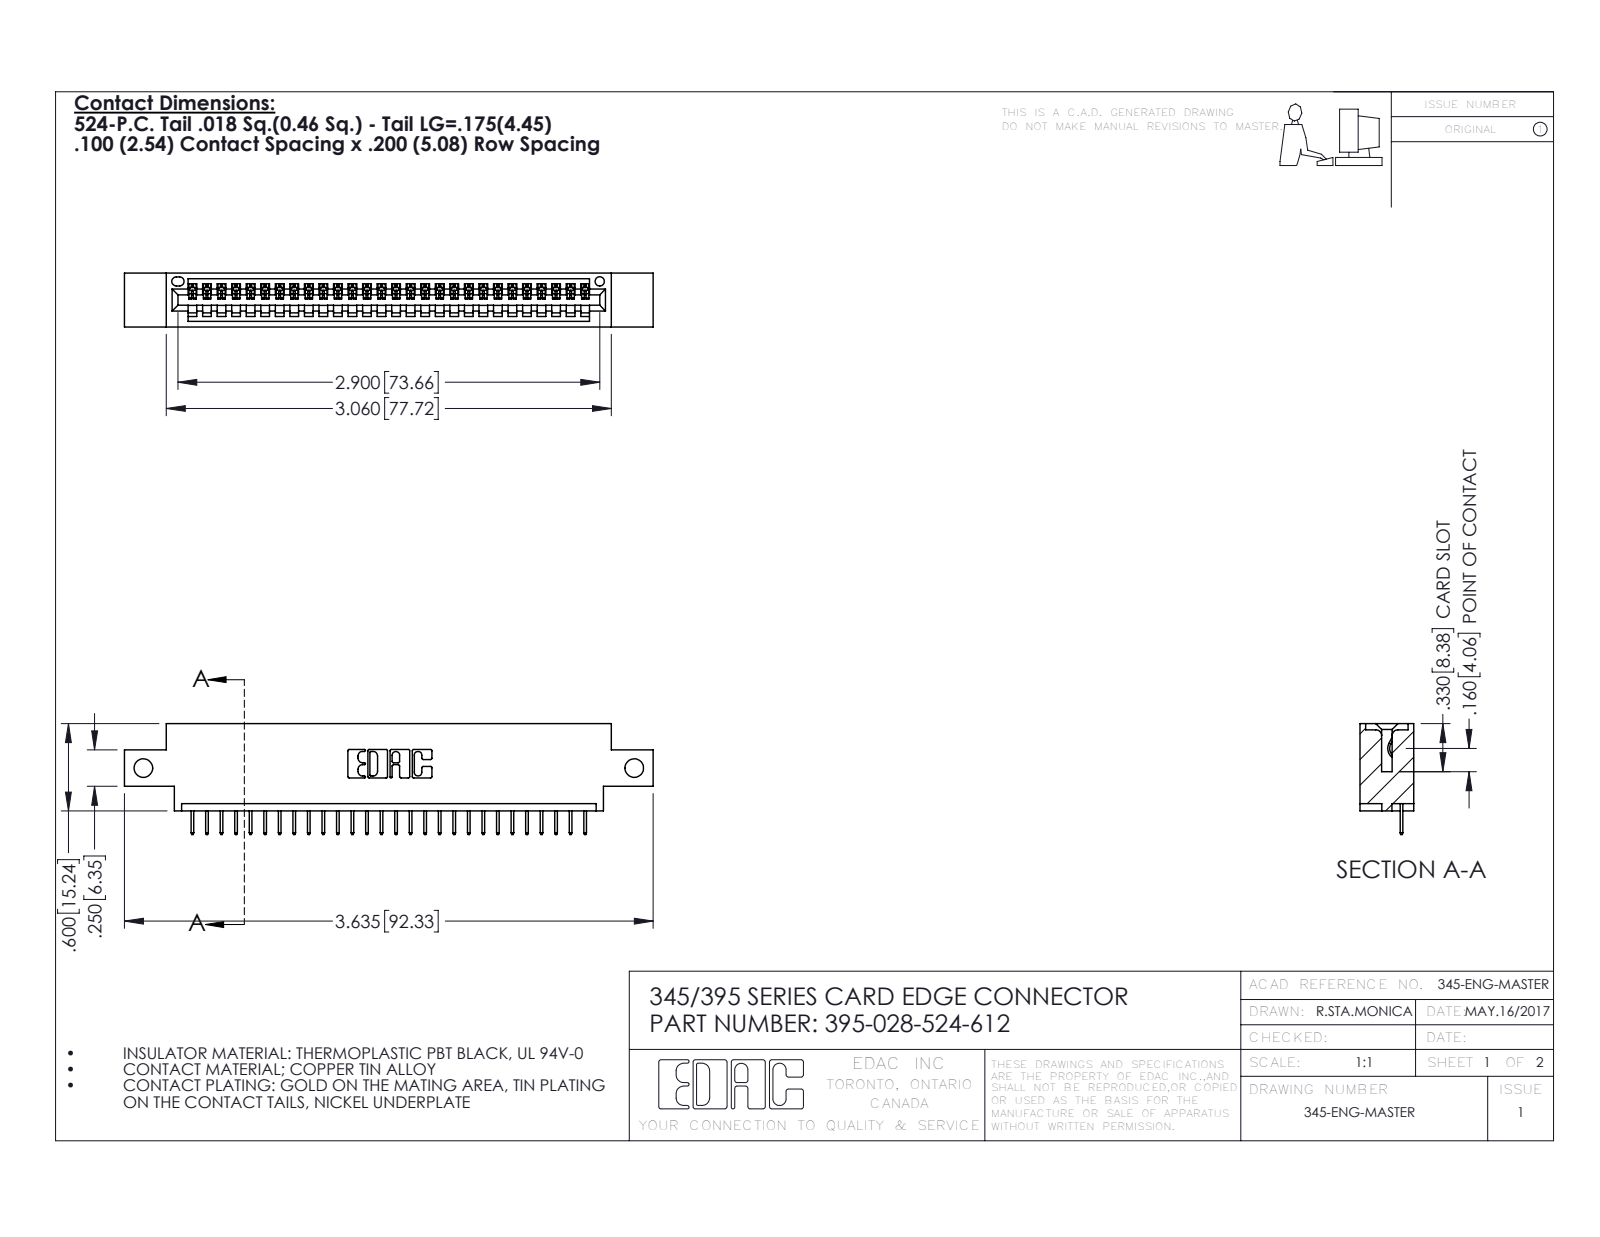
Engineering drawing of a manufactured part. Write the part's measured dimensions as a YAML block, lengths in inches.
part_name: "345-292-001_345-293-124; 345 Part_0.170 Offset - Side Mount; 395-028-524-612"
step_written_by: "SolidWorks 2016 (CONFIG_CONTROL_DESIGN)"
units: inches
bodies: {solids: 29, faces: 1866, planar: 1372, cylindrical: 494, other: 0}
overall_size: [3.635, 0.762, 0.37]
volume: 0.509
surface_area: 16.32
round_holes:
  - {diameter: 0.128, count: 2}
  - {diameter: 0.064, count: 1}
partial_cylinders:
  - {radius: 0.006, count: 56}
  - {radius: 0.01, count: 22}
  - {radius: 0.007, count: 6}
  - {radius: 0.031, count: 6}
  - {radius: 0.026, count: 3}
  - {radius: 0.031, count: 2}
  - {radius: 0.04, count: 2}
  - {radius: 0.014, count: 1}
face_to_face_distances: [0.072, 0.298, 0.37, 0.2, 0.098, 0.272, 0.025, 0.225, 0.072, 0.175]
hole_center_spacings: [3.375]
